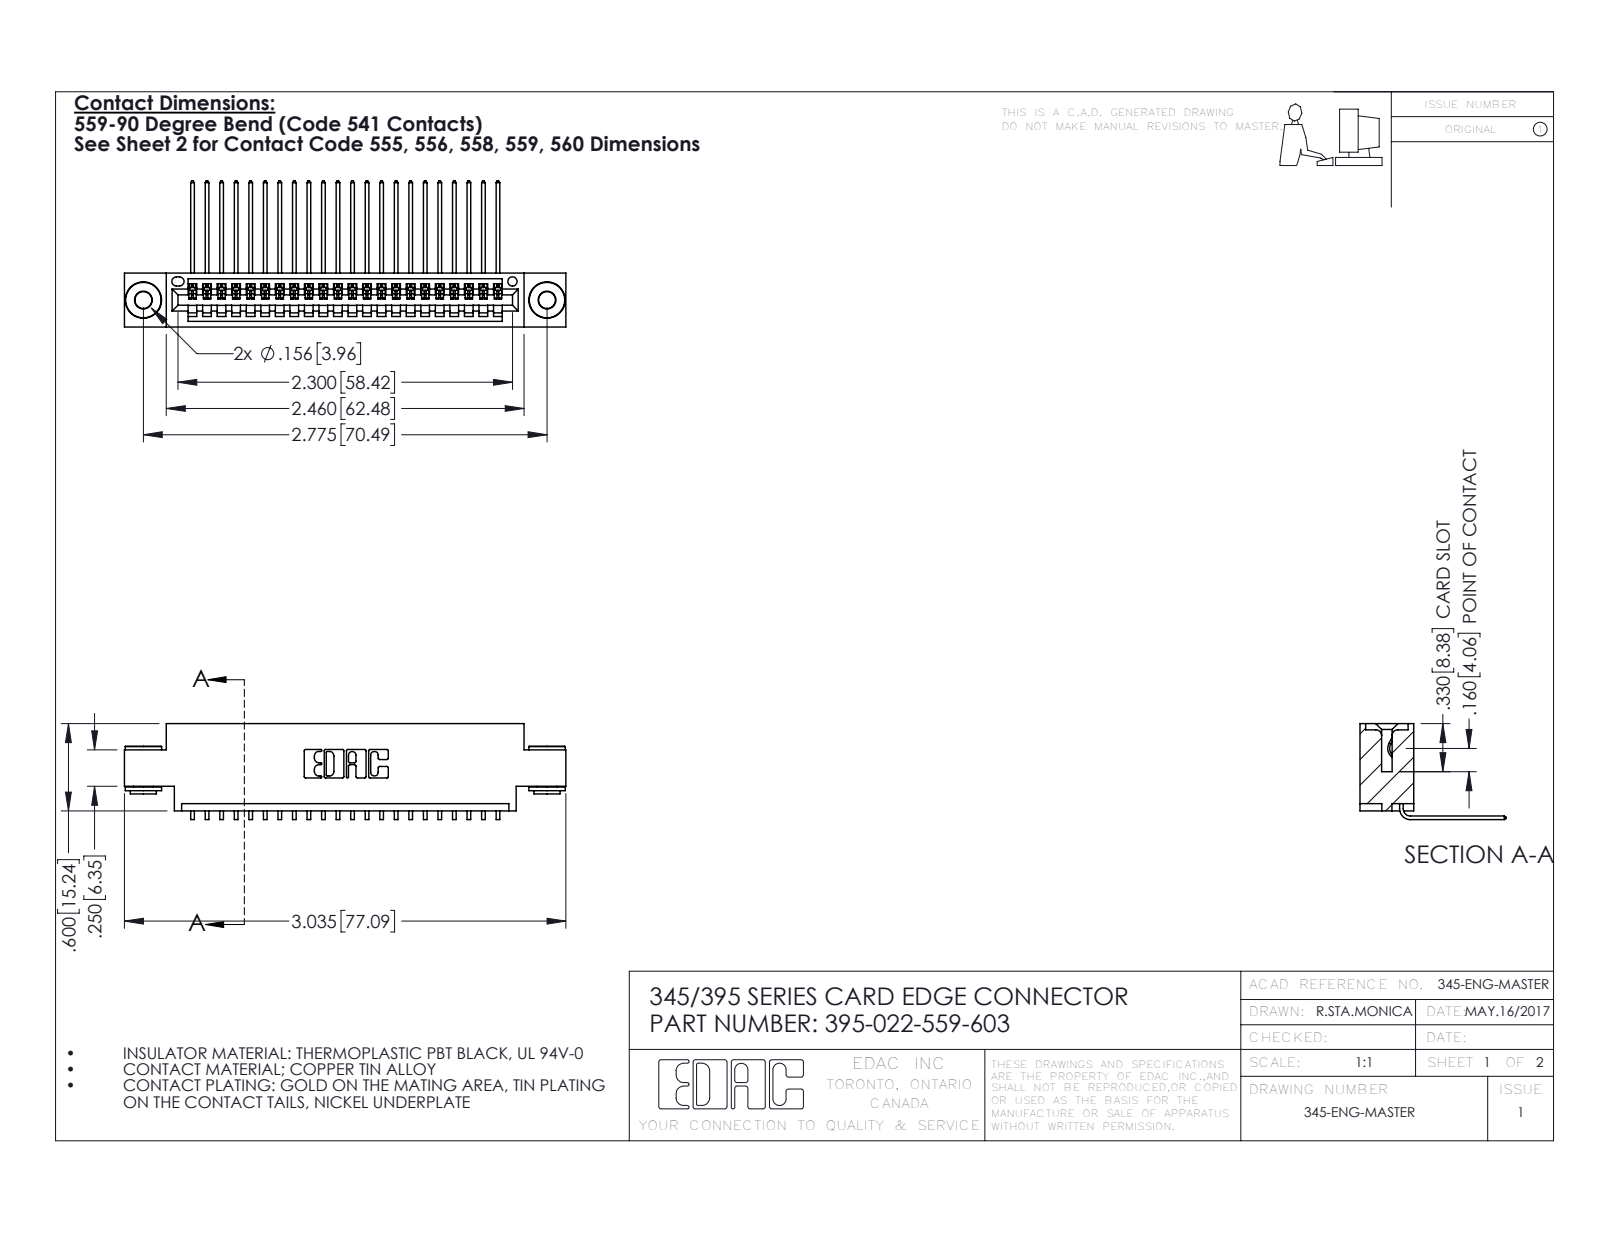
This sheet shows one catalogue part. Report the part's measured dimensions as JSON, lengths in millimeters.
{"part_name": "345-292-001_558 559 Tail - 1; 345 Part_0.170 Offset - 0.156 Dia-TH; 395-022-559-603; 345-250-002_345-250-002-102", "step_written_by": "SolidWorks 2016 (CONFIG_CONTROL_DESIGN)", "units": "millimeters", "bodies": {"solids": 25, "faces": 1488, "planar": 1018, "cylindrical": 462, "other": 8}, "overall_size": [77.1, 25.5, 16.7], "volume_mm3": 7140, "surface_area_mm2": 9987, "round_holes": [[2.9, 2], [4, 2], [1.6, 1]], "round_bosses_or_shafts": [[6.4, 2], [4.6, 2], [3.5, 2]], "partial_cylinders_radius": [[0.2, 44], [0.3, 22], [0.2, 6], [0.8, 6], [0.7, 3], [0.8, 2], [1, 2], [0.4, 1]], "face_to_face_distances": [9.4, 1.8, 7.6, 5.1, 2.5, 6.9, 0.6, 5.7, 4.4, 2.5], "hole_center_spacings": [6.9, 64.5, 70.5]}
